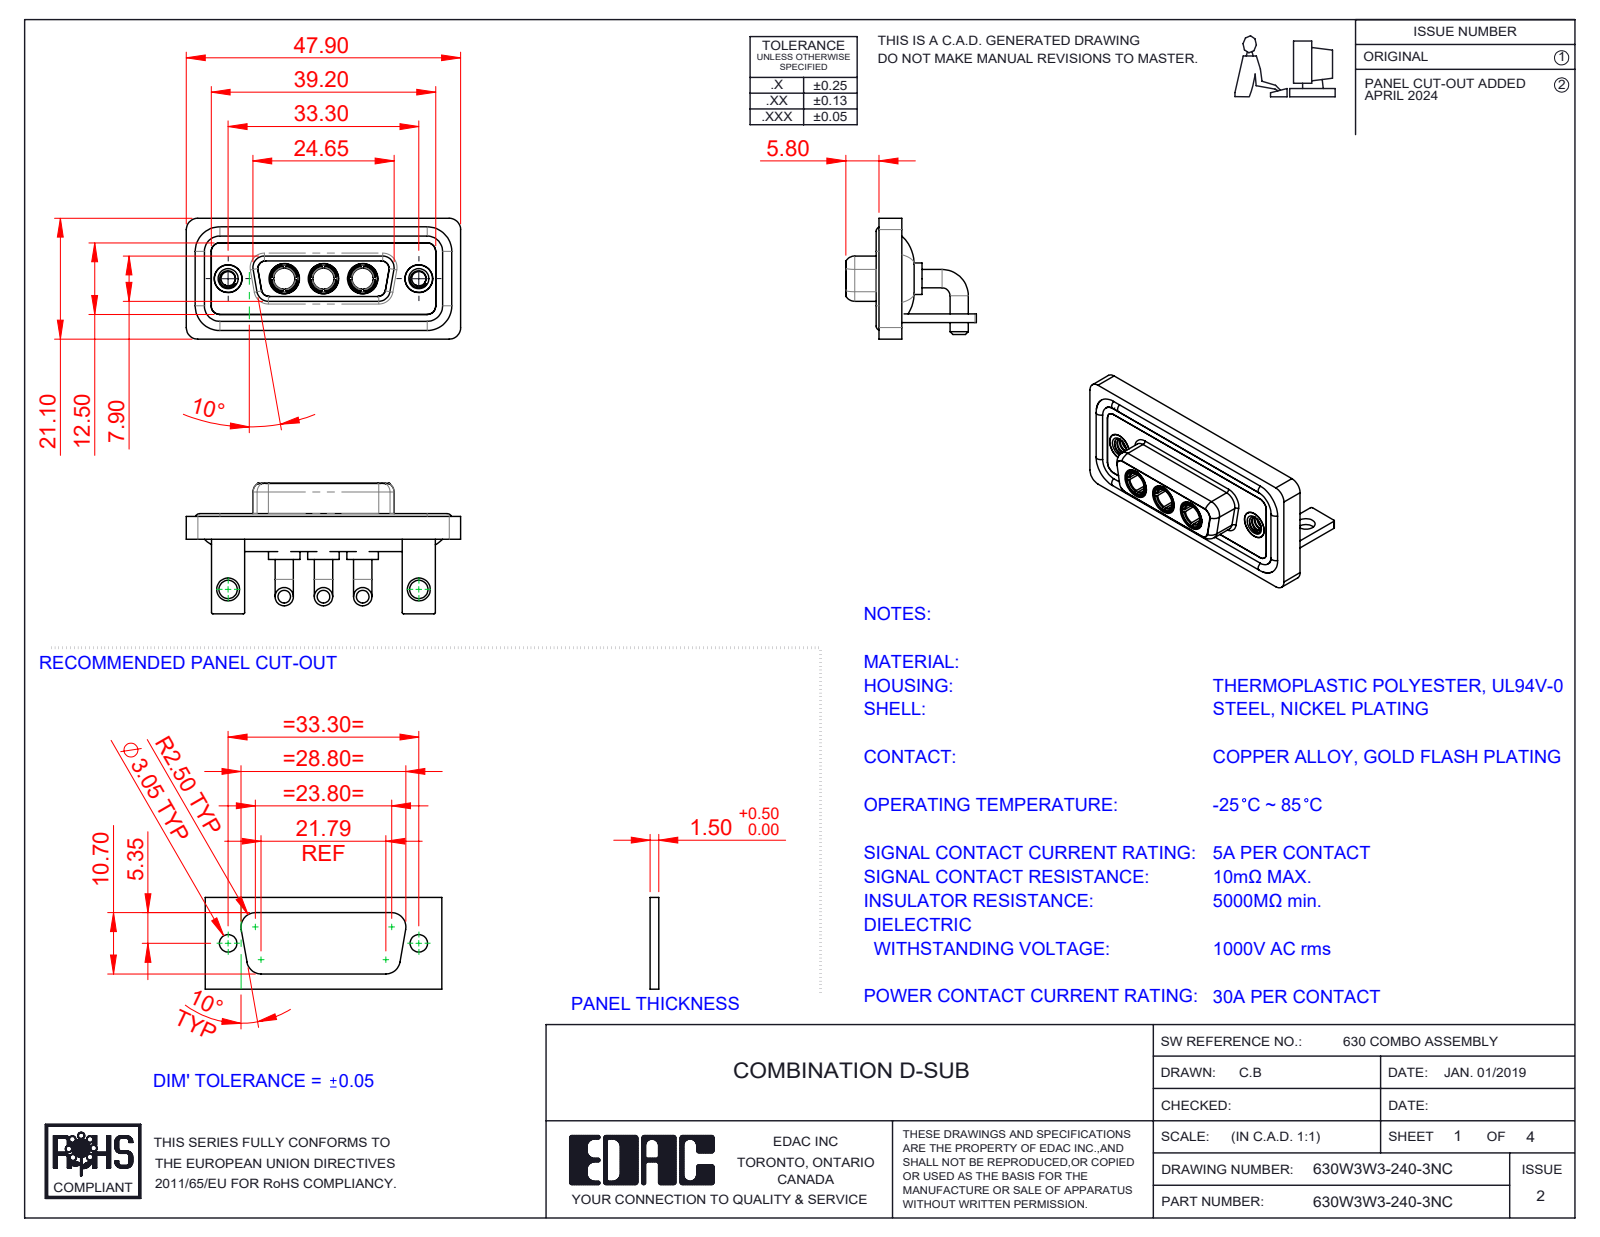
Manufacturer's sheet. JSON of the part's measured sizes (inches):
{"part_name": "630W3W3-240-3NC; 630Combo Shell Rear_15 Contacts; 630Combo Stabilizer Bracket_50 Contacts; 630Combo Threaded Rivet_A (+4 more)", "step_written_by": "SolidWorks 2023 (CONFIG_CONTROL_DESIGN)", "units": "inches", "bodies": {"solids": 15, "faces": 662, "planar": 212, "cylindrical": 285, "other": 165}, "overall_size": [1.886, 0.898, 0.831], "volume_in3": 0.404, "surface_area_in2": 16.69, "round_holes": [[0.191, 5], [0.146, 3], [0.209, 3], [0.098, 2], [0.126, 2], [0.157, 2], [0.159, 2], [0.197, 2]], "round_bosses_or_shafts": [[0.126, 6], [0.063, 4], [0.217, 3], [0.205, 3], [0.195, 3], [0.187, 3], [0.148, 3], [0.195, 2]], "partial_cylinders_radius": [[0.079, 21], [0.059, 18], [0.01, 16], [0.053, 12], [0.063, 8], [0.02, 5], [0.024, 4], [0.026, 4]], "face_to_face_distances": [0.016, 0.114, 0.059, 0.071, 0.146, 0.043, 0.161, 0.063, 0.098, 0.055], "hole_center_spacings": [0.27, 0.386, 0.656, 0.925, 1.311, 0.539]}
